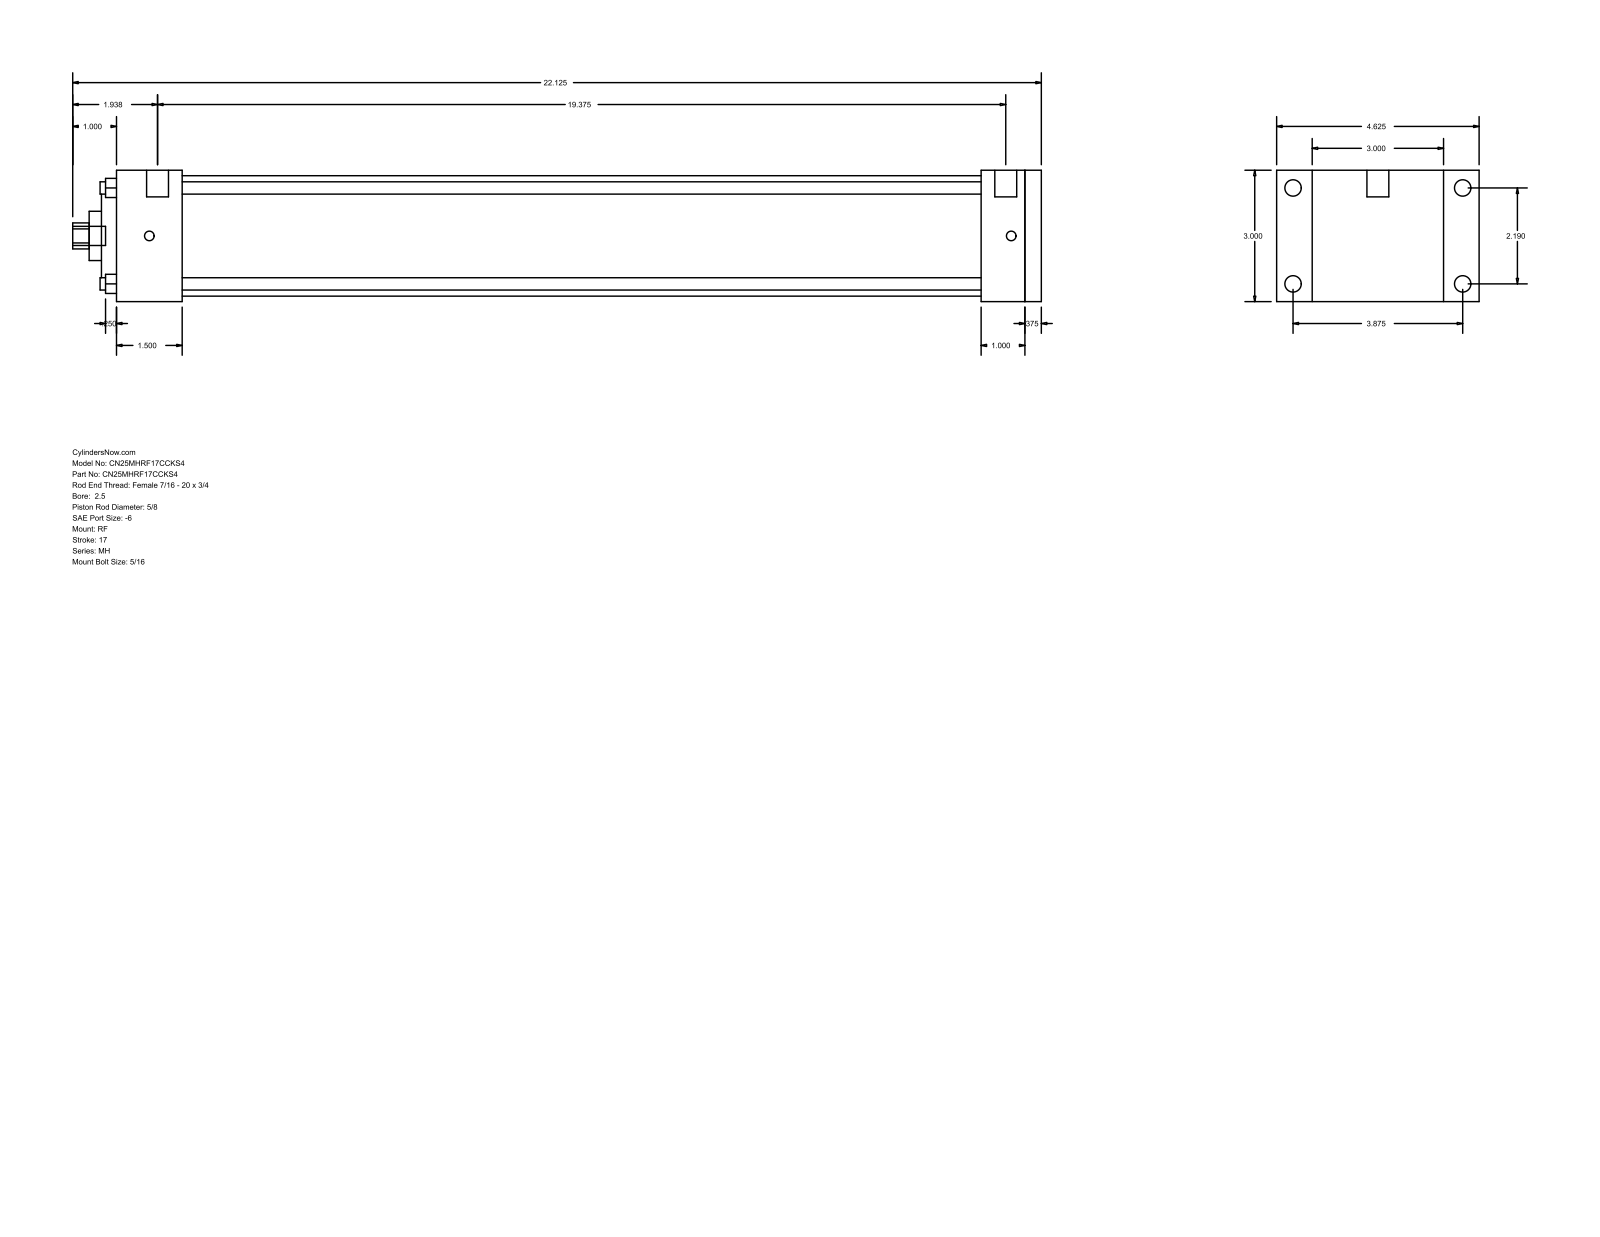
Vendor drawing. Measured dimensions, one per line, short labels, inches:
name: MH_RF__0250_0.625
written by: GSSL Pune (CONFIG_CONTROL_DESIGN)
unit: in
bodies: 0 solids, 94 faces (65 planar, 29 cylindrical, 0 other)
size: 22.125 × 4.625 × 3
holes: 4× ⌀0.281, 1× ⌀0.625, 1× ⌀1.125, 1× ⌀2.187, 1× ⌀2.75
bosses: 4× ⌀0.375, 4× ⌀0.219, 2× ⌀0.5, 1× ⌀0.437
rounds: 1× R0.297
face distances: 3, 0.375, 21.125, 20.75, 1, 19.75, 1.375, 1.5, 18.25, 19.25
hole spacings: 1.548, 2.19, 3.097
